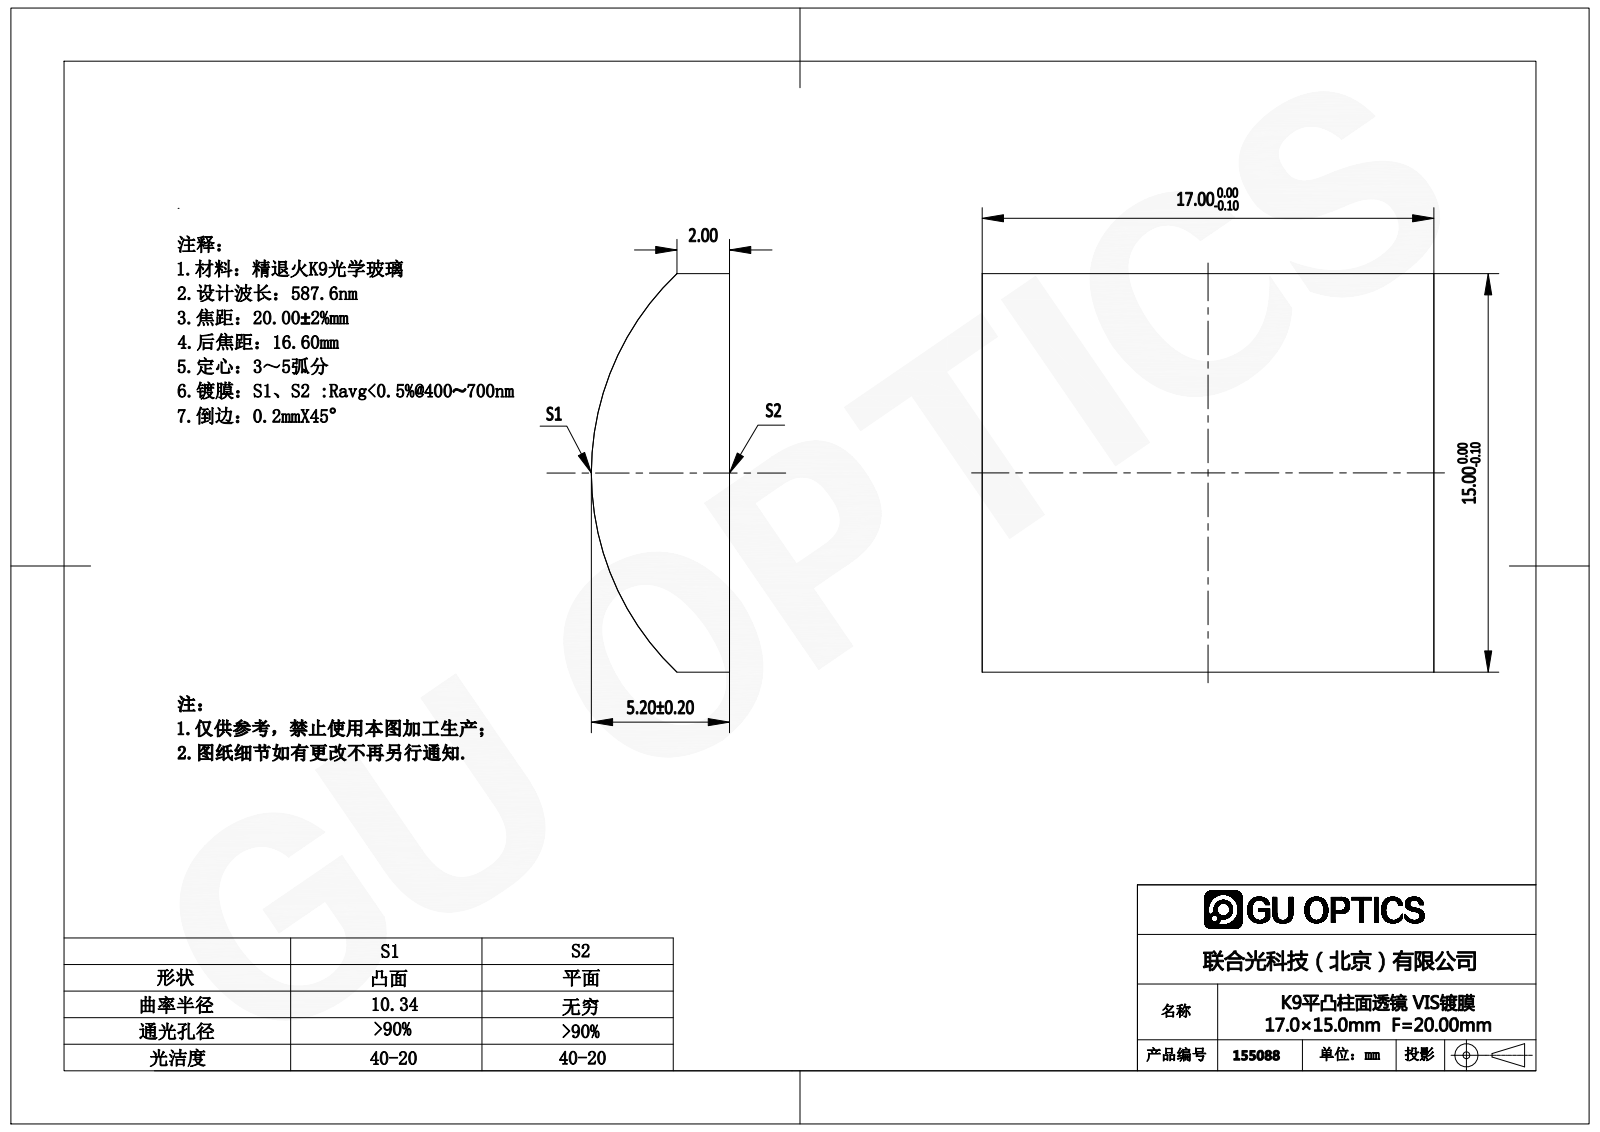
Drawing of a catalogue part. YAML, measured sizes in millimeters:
part_name: "155022"
step_written_by: "SolidWorks 2016 (AUTOMOTIVE_DESIGN)"
units: millimeters
bodies: {solids: 1, faces: 6, planar: 5, cylindrical: 1, other: 0}
overall_size: [17, 15, 5.2]
volume: 1072
surface_area: 734
partial_cylinders:
  - {radius: 10.34, count: 1}
face_to_face_distances: [17, 15]
